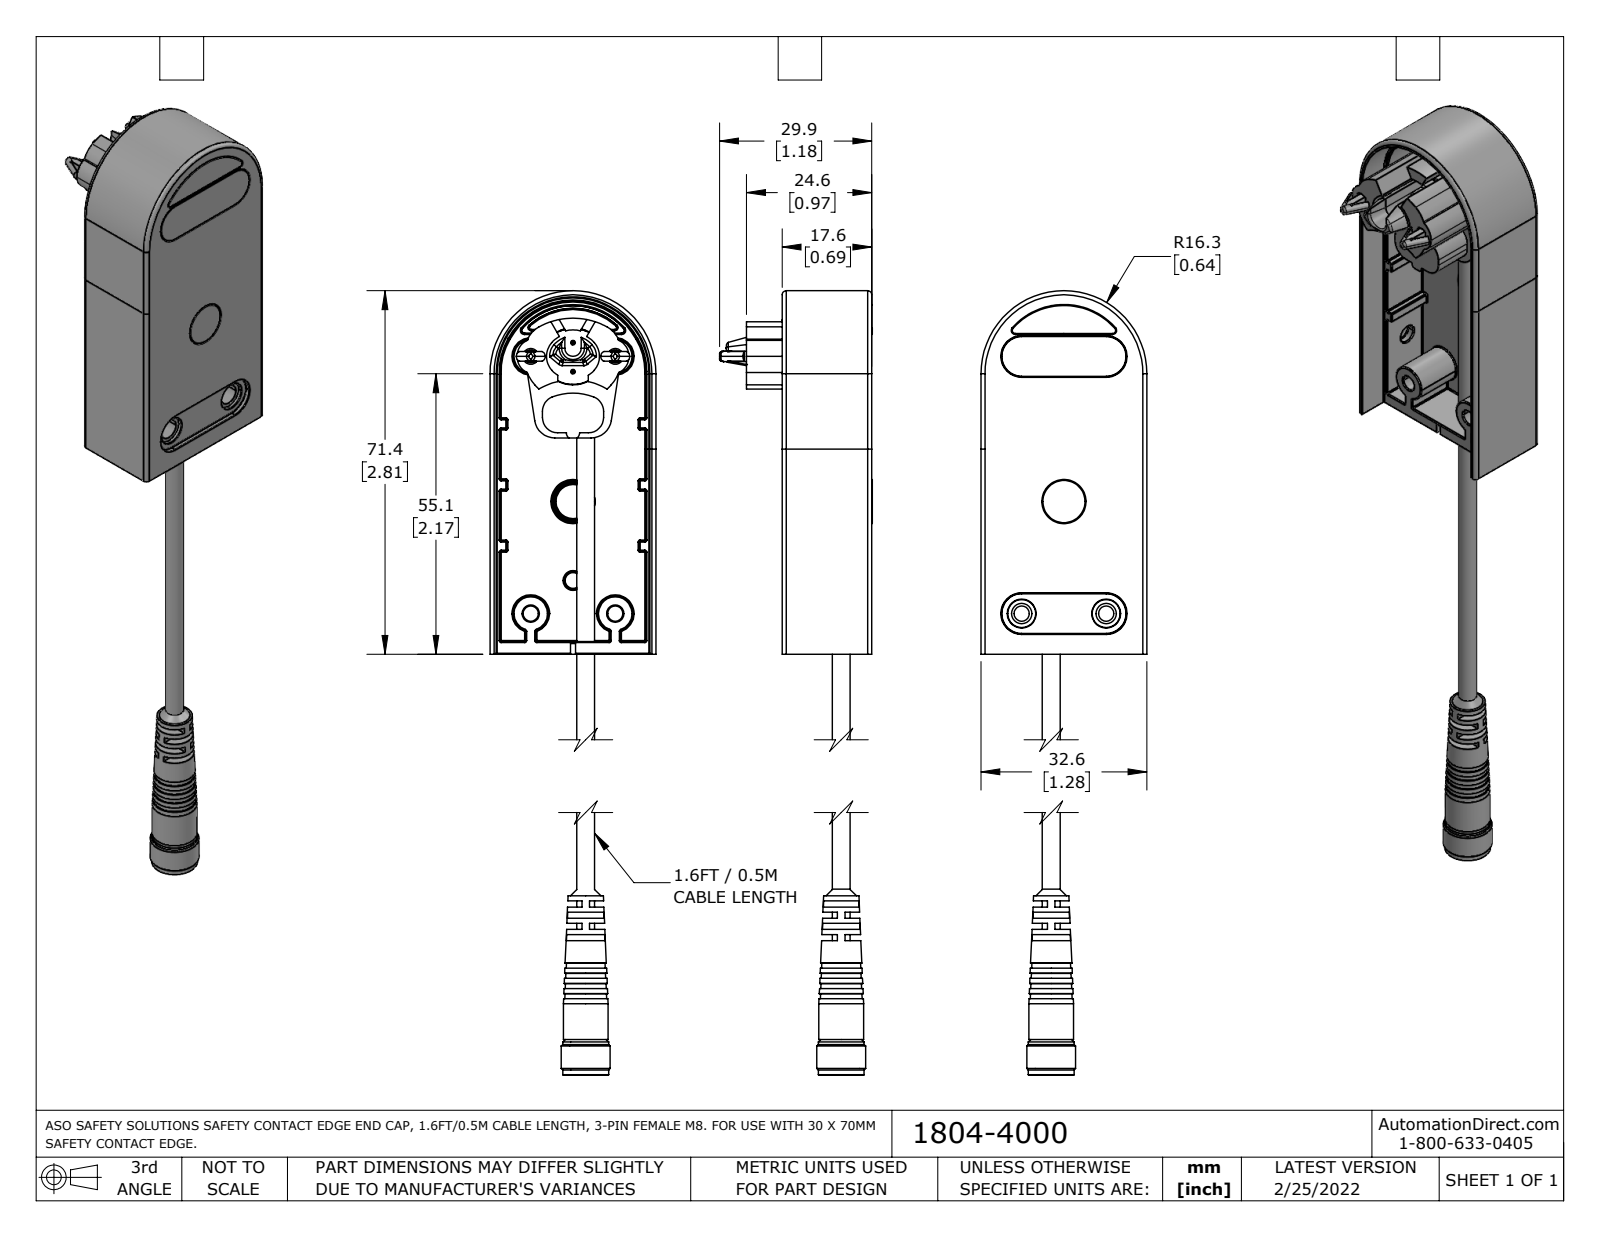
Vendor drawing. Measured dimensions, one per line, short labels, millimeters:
name: 1804-4000_Default
written by: SolidWorks 2021 (CONFIG_CONTROL_DESIGN)
unit: mm
bodies: 11 solids, 1022 faces (254 planar, 435 cylindrical, 333 other)
size: 172.3 × 32.6 × 30
volume: 17 631 mm³; area: 20 469 mm²
holes: 4× ⌀0.5, 4× ⌀5.5, 3× ⌀0.8, 3× ⌀0.85, 3× ⌀1.6, 3× ⌀3.5, 3× ⌀4, 2× ⌀3, 2× ⌀3.1, 1× ⌀3.4, 1× ⌀4, 1× ⌀5.9
bosses: 13× ⌀1.2, 6× ⌀0.5, 3× ⌀3.5, 3× ⌀1, 2× ⌀7, 2× ⌀5, 2× ⌀2.5, 2× ⌀2
rounds: 75× R0.2, 17× R0.1, 12× R1, 6× R0.3, 6× R3, 6× R3.5, 6× R4, 5× R0.5
face distances: 1.8, 2, 0.8, 32.6, 30.6, 1.2, 31.4, 29.4, 1, 28.6
hole spacings: 16.6, 1.4, 1.75, 2.47, 8.73, 8.83, 10.54, 22.14
